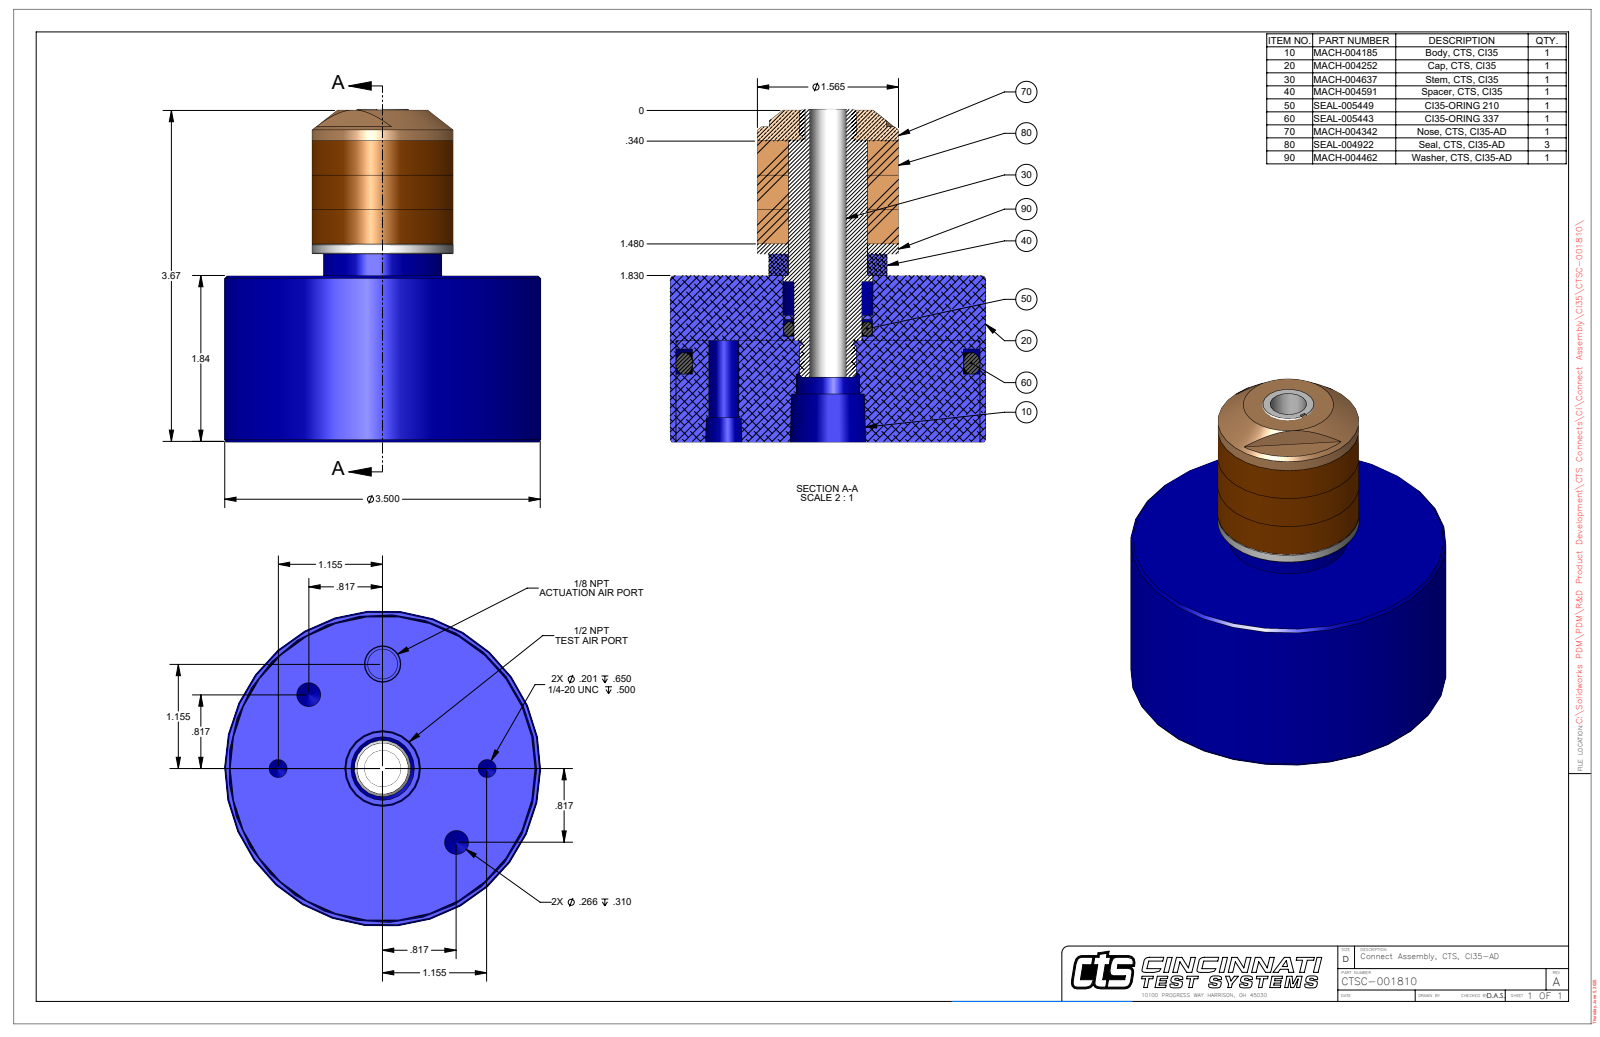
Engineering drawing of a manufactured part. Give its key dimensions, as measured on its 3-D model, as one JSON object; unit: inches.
{"part_name": "CTSC-001810", "step_written_by": "SolidWorks 2023 (AUTOMOTIVE_DESIGN)", "units": "inches", "bodies": {"solids": 1, "faces": 74, "planar": 20, "cylindrical": 27, "other": 27}, "overall_size": [3.68, 3.5, 3.5], "volume_in3": 20, "surface_area_in2": 71.05, "round_holes": [[0.201, 2], [0.266, 2], [0.332, 1], [0.406, 1], [0.703, 1], [3.373, 1]], "round_bosses_or_shafts": [[3.5, 1], [3.365, 1], [1.565, 1], [1.565, 1], [1.312, 1]], "partial_cylinders_radius": [[0.266, 1]], "face_to_face_distances": [1.84, 2.08, 0.24, 3.67, 1.83, 1.59, 0.719, 1.121, 1.361, 2.951], "hole_center_spacings": [0.884, 1.155, 2.134, 1.155, 1.633, 2.309, 2.31]}
